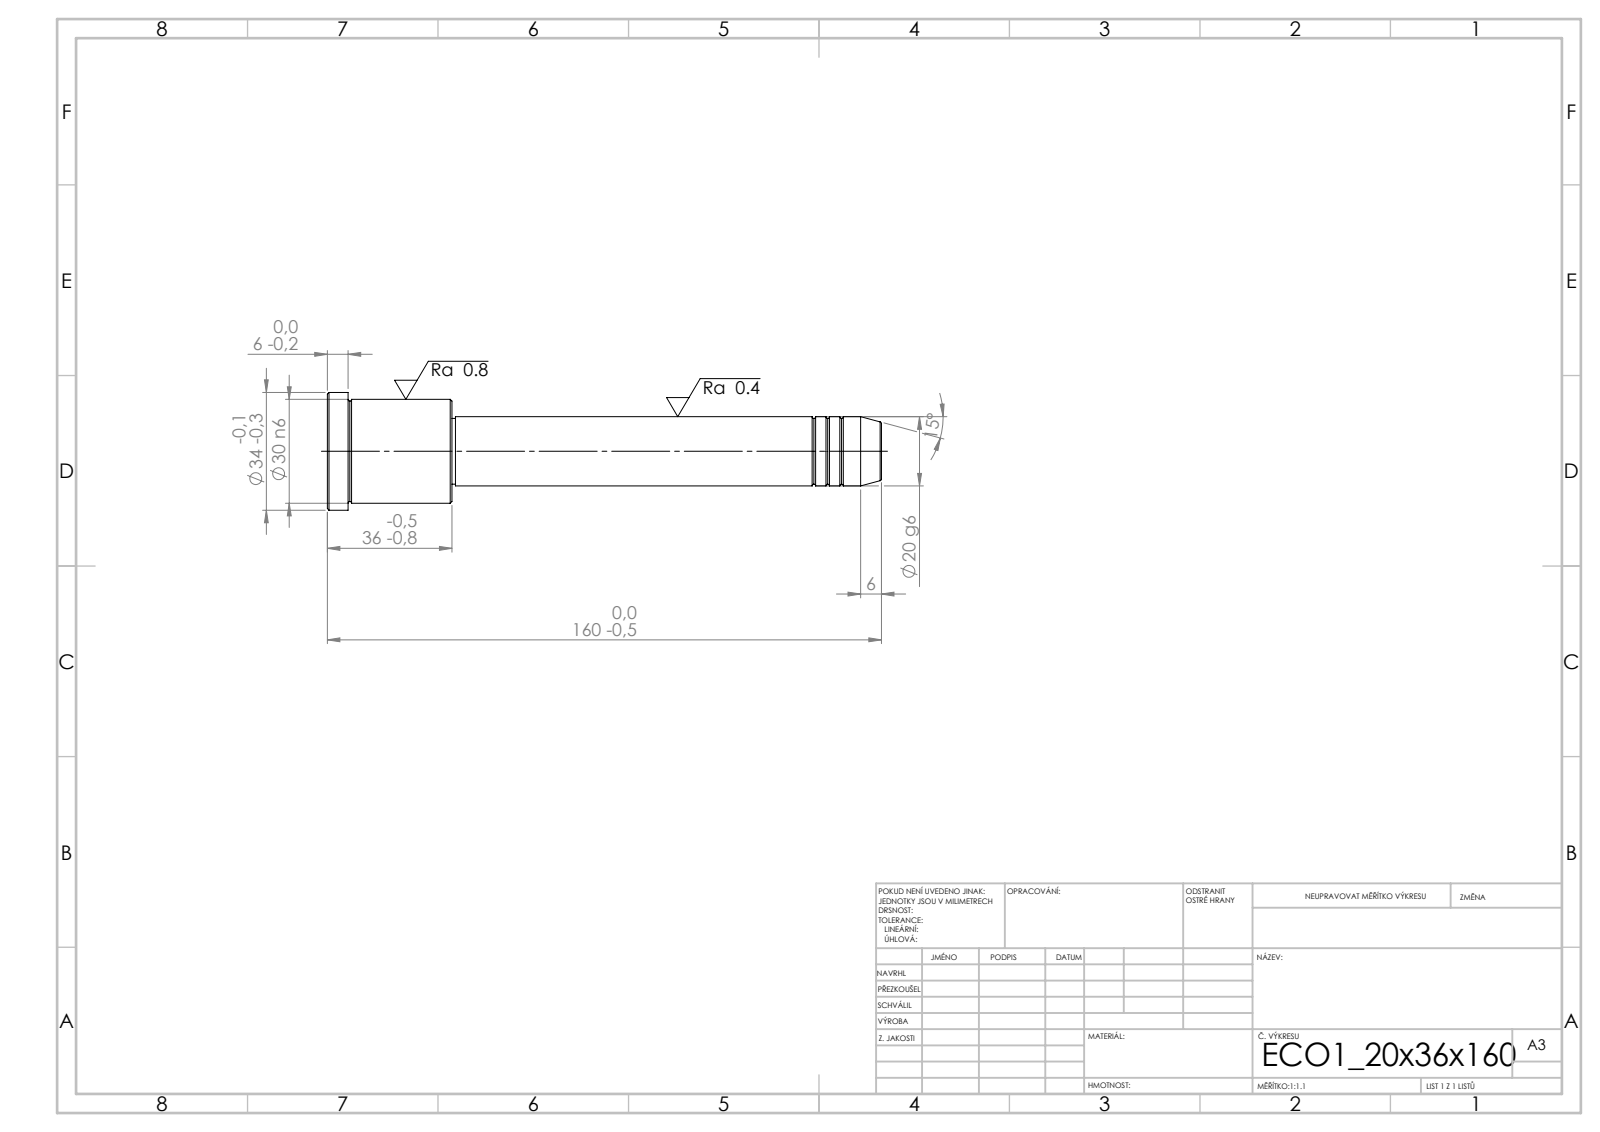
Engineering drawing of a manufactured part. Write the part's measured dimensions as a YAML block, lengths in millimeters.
step_written_by: "SolidWorks 2019 (CONFIG_CONTROL_DESIGN)"
units: millimeters
bodies: {solids: 1, faces: 43, planar: 5, cylindrical: 14, other: 24}
overall_size: [160, 34, 34]
volume: 65156
surface_area: 13106
round_bosses_or_shafts:
  - {diameter: 34, count: 1}
  - {diameter: 30, count: 1}
  - {diameter: 20, count: 1}
  - {diameter: 19, count: 1}
face_to_face_distances: [36, 124, 160, 154, 30, 6, 123, 1, 31, 37]
